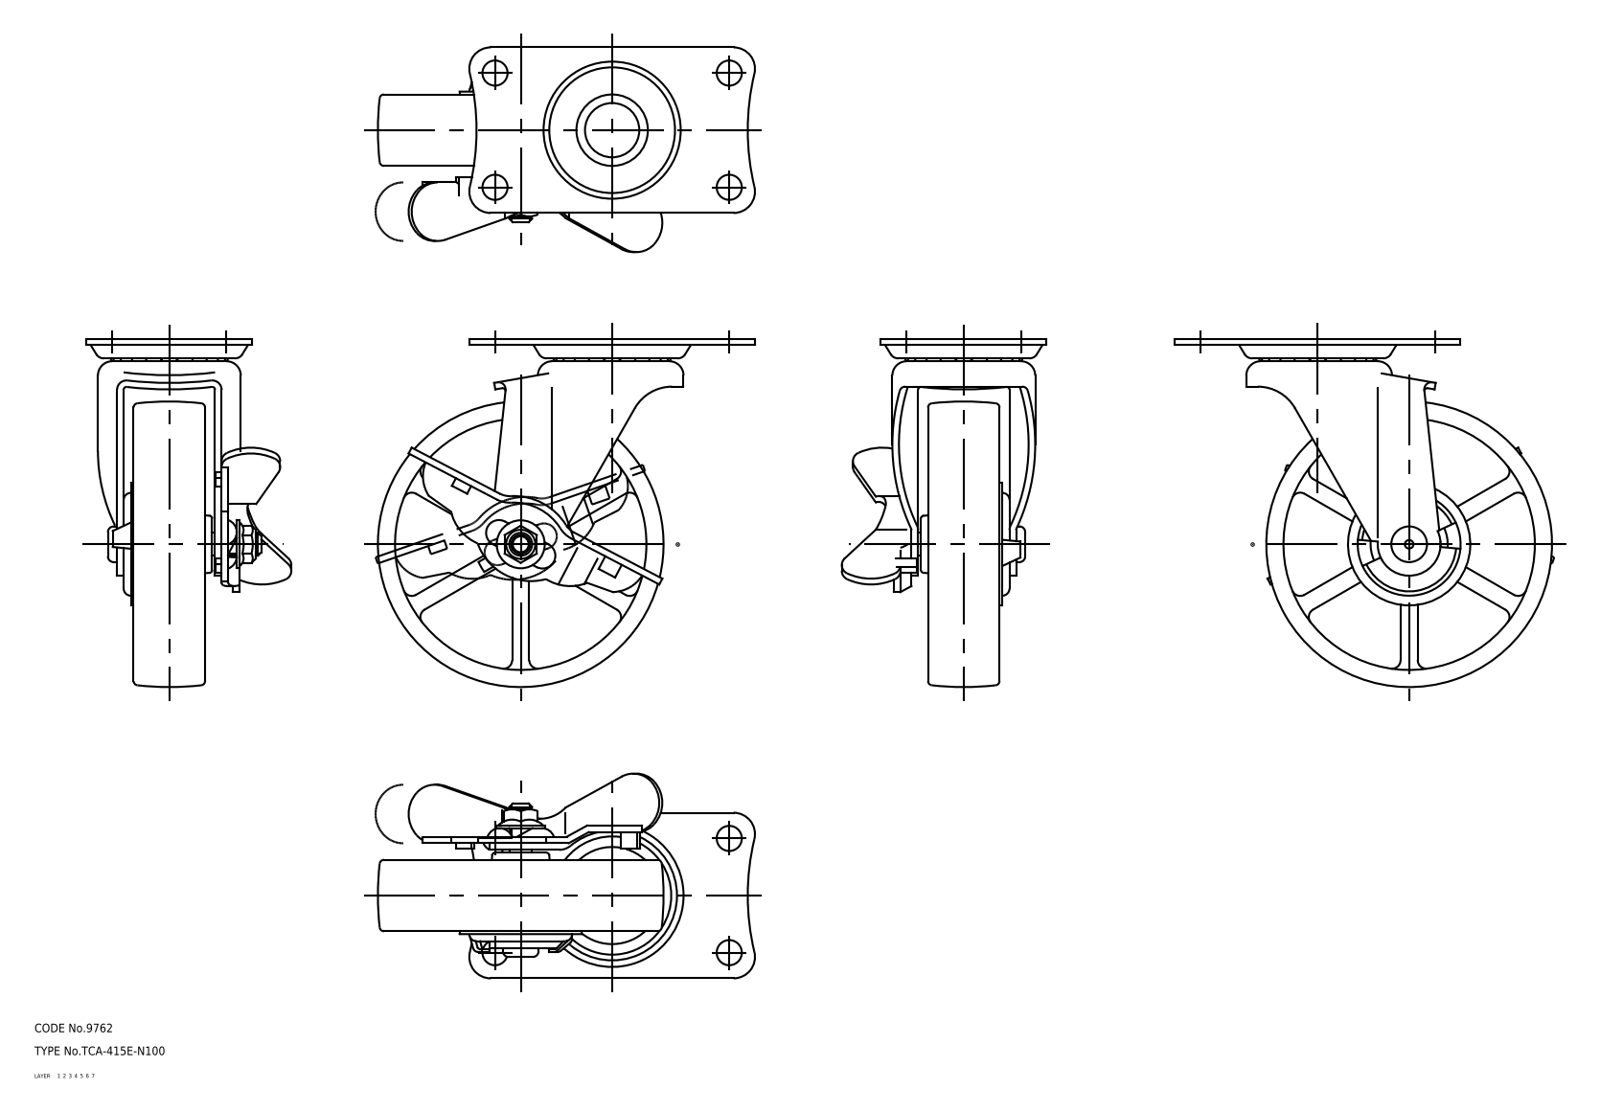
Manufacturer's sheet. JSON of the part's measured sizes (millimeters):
{"part_name": "wheel; mounting plate; main shaft; lever (+2 more)", "step_written_by": "CADfix (AUTOMOTIVE_DESIGN)", "units": "millimeters", "bodies": {"solids": 6, "faces": 663, "planar": 0, "cylindrical": 0, "other": 663}, "overall_size": [132, 122, 71.7], "volume_mm3": 195859, "surface_area_mm2": 71694}
